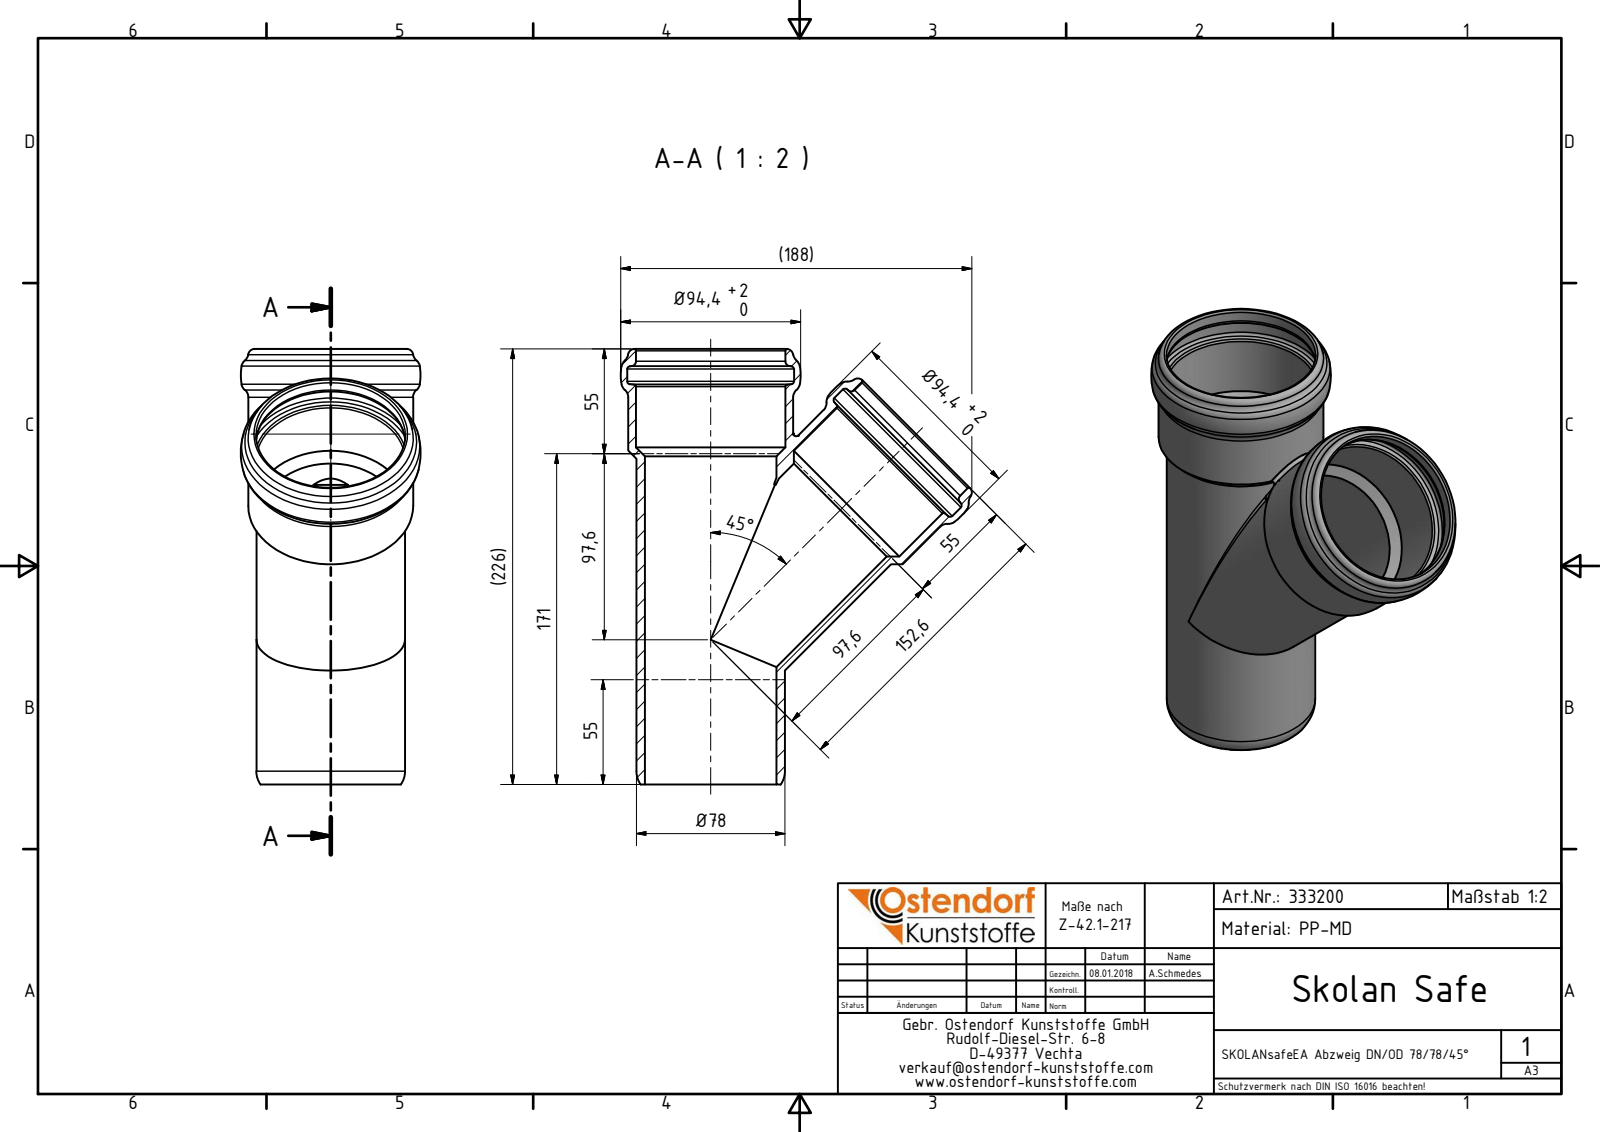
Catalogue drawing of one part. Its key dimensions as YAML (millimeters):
part_name: "333200 SKOLANsafeEA Abzweiger DN_OD 78_78_45°"
step_written_by: "Autodesk Inventor 2016 (AUTOMOTIVE_DESIGN)"
units: millimeters
bodies: {solids: 1, faces: 50, planar: 4, cylindrical: 13, other: 33}
overall_size: [228.61, 184.36, 94.4]
volume: 339574
surface_area: 160194
round_holes:
  - {diameter: 69, count: 2}
  - {diameter: 78.4, count: 2}
  - {diameter: 87.6, count: 2}
round_bosses_or_shafts:
  - {diameter: 86.6, count: 2}
  - {diameter: 78, count: 2}
